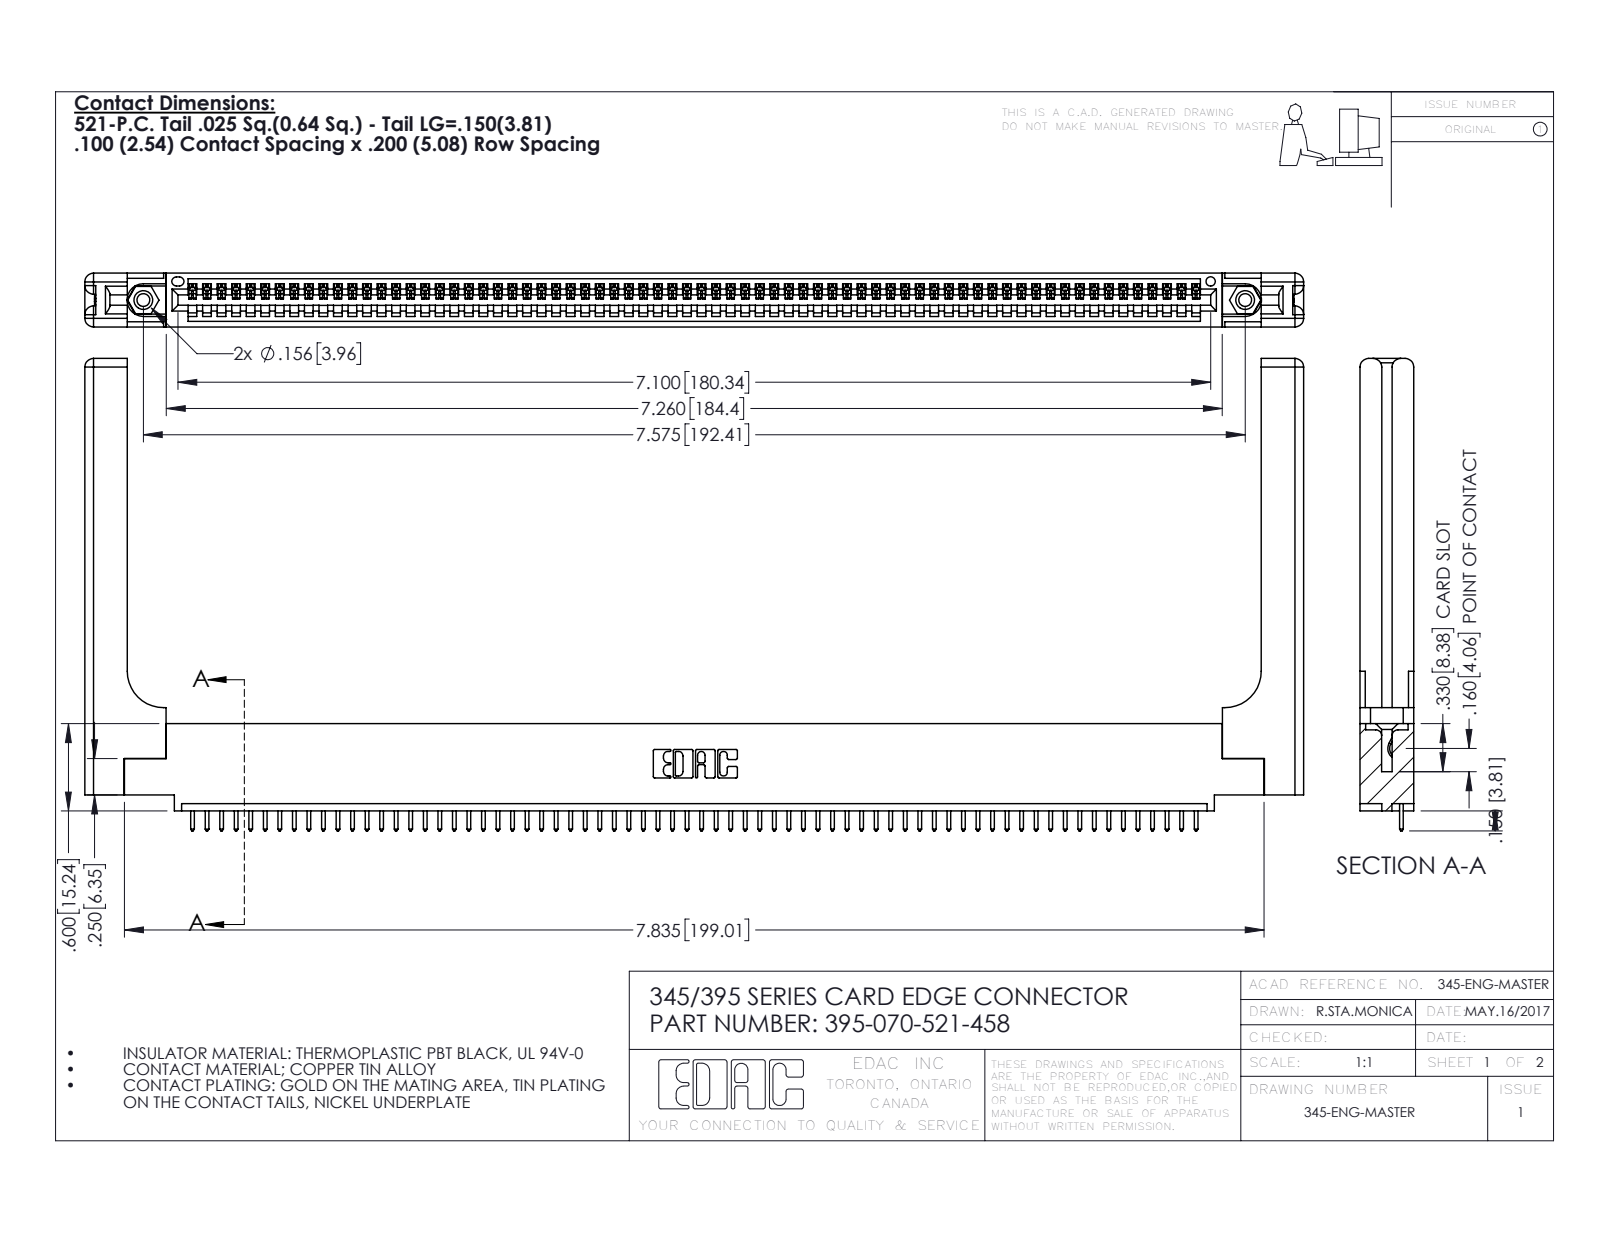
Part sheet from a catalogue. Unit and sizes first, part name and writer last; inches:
Units: inches
Overall size (bounding box): 8.379 × 3.247 × 0.37
Round holes (diameter × count): ⌀0.089 ×2, ⌀0.125 ×2, ⌀0.156 ×2, ⌀0.064 ×1
Round bosses / shafts (diameter × count): ⌀0.155 ×2
Partial cylindrical surfaces — rounded edges, fillets, slot ends (radius × count): R0.006 ×140, R0.01 ×140, R0.01 ×22, R0.06 ×16, R0.007 ×6, R0.031 ×6, R0.026 ×3, R0.03 ×2
Main face-to-face distances: 0.072, 0.298, 0.37, 0.098, 0.272, 0.025, 0.2, 0.225, 0.148, 0.15
Hole centre spacings: 0.27, 7.339, 7.575
Volume: 1.75 in³ · Surface area: 49.28 in²
Bodies: 75 solids, 4446 faces (3032 planar, 1354 cylindrical, 60 other)
Part name (STEP PRODUCT): 345-250-001_345-250-001-102; 345-220-058_345-220-058; 395-070-521-458; 345-292-001_345-293-121 (+1 more)
STEP written by: SolidWorks 2016 (CONFIG_CONTROL_DESIGN)
